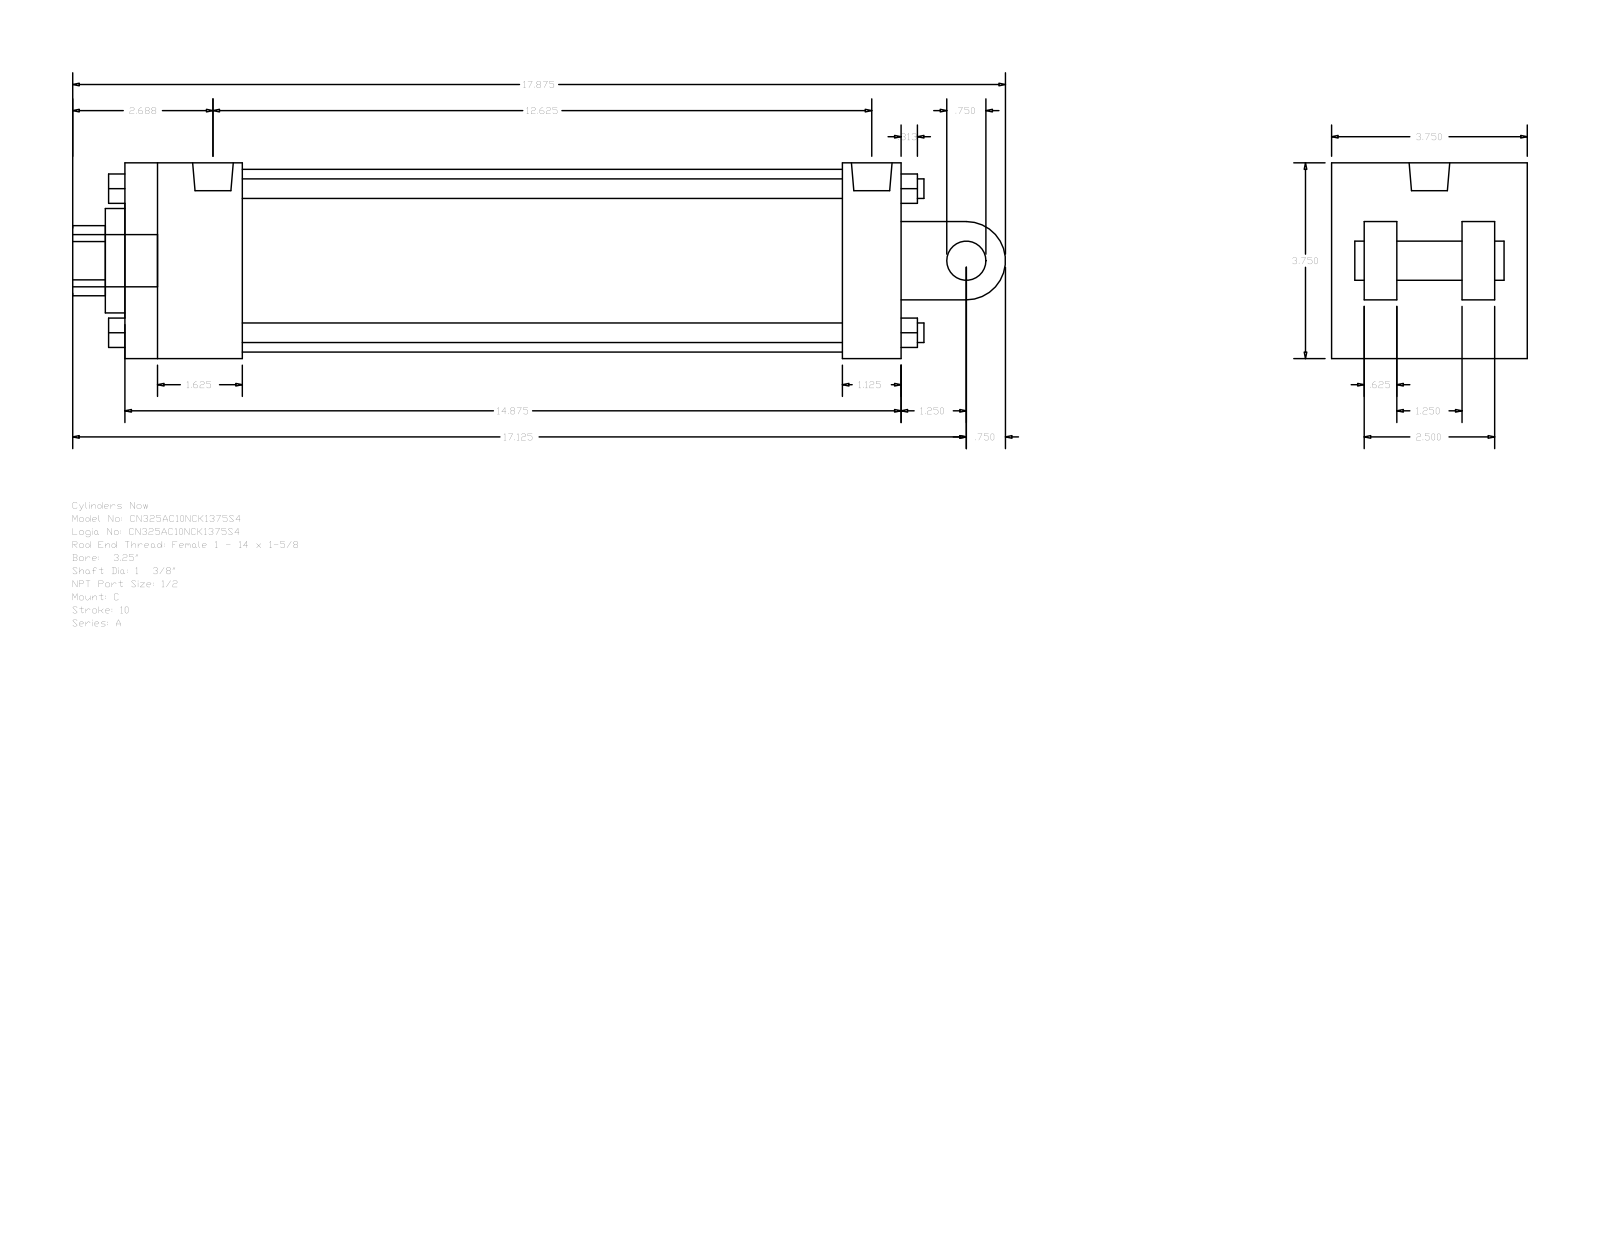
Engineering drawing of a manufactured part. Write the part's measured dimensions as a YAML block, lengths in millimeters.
part_name: "A_C__0325_1.375"
step_written_by: "GSSL Pune (CONFIG_CONTROL_DESIGN)"
units: millimeters
bodies: {solids: 0, faces: 135, planar: 102, cylindrical: 33, other: 0}
overall_size: [454.02, 95.25, 95.25]
round_holes:
  - {diameter: 8.73, count: 2}
  - {diameter: 19.77, count: 1}
  - {diameter: 34.92, count: 1}
  - {diameter: 50.8, count: 1}
  - {diameter: 88.9, count: 1}
round_bosses_or_shafts:
  - {diameter: 9.53, count: 4}
  - {diameter: 8.73, count: 2}
  - {diameter: 25.4, count: 1}
  - {diameter: 19.77, count: 1}
  - {diameter: 19.05, count: 1}
partial_cylinders:
  - {radius: 17.06, count: 1}
  - {radius: 19.05, count: 1}
face_to_face_distances: [95.24, 15.87, 377.83, 63.5, 66.67, 28.58, 79.37, 31.74, 47.63, 349.25]
hole_center_spacings: [3.18]
